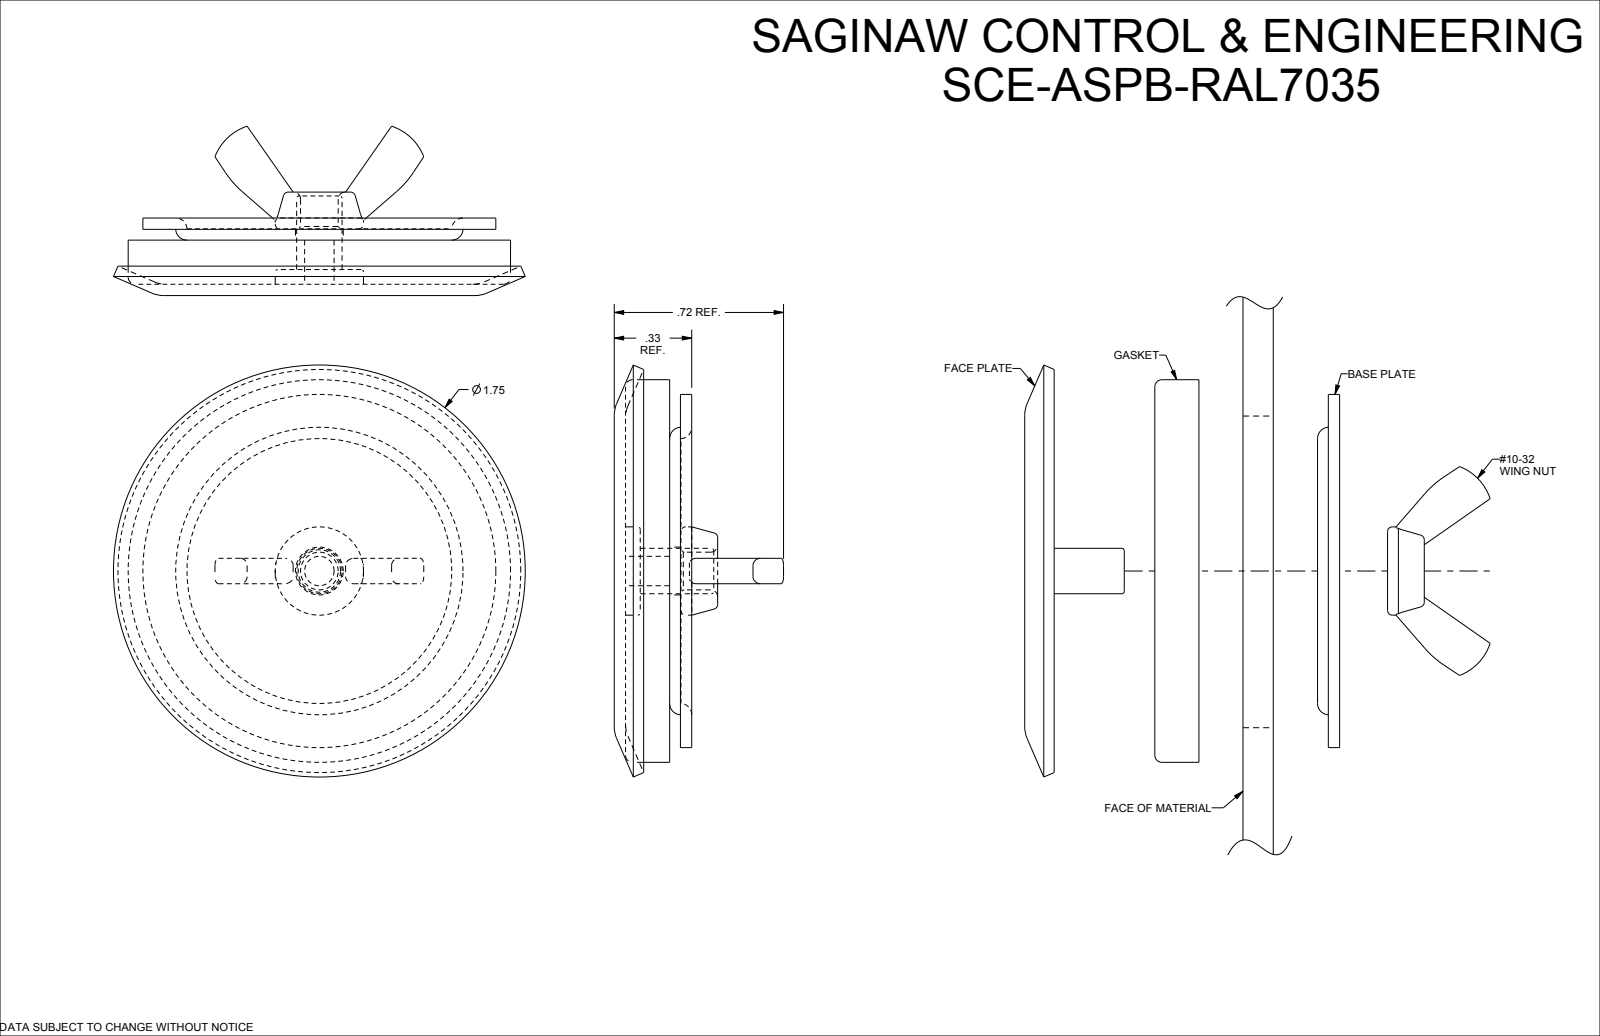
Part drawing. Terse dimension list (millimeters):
name: SCE-ASPB-RAL7035
written by: SolidWorks 2019 (CONFIG_CONTROL_DESIGN)
unit: mm
bodies: 5 solids, 72 faces (27 planar, 24 cylindrical, 21 other)
size: 44.5 × 44.5 × 18.3
volume: 10 300 mm³; area: 9 910 mm²
holes: 1× ⌀3.2, 1× ⌀4.1, 1× ⌀5.2
bosses: 1× ⌀41.3, 1× ⌀38.1, 1× ⌀9.5, 1× ⌀4.9
rounds: 12× R0.8, 2× R5.6, 2× R10.2
face distances: 4.7, 1.2, 6, 1.2, 7.1, 7.2, 2.4, 8.4, 5.9, 2.7
